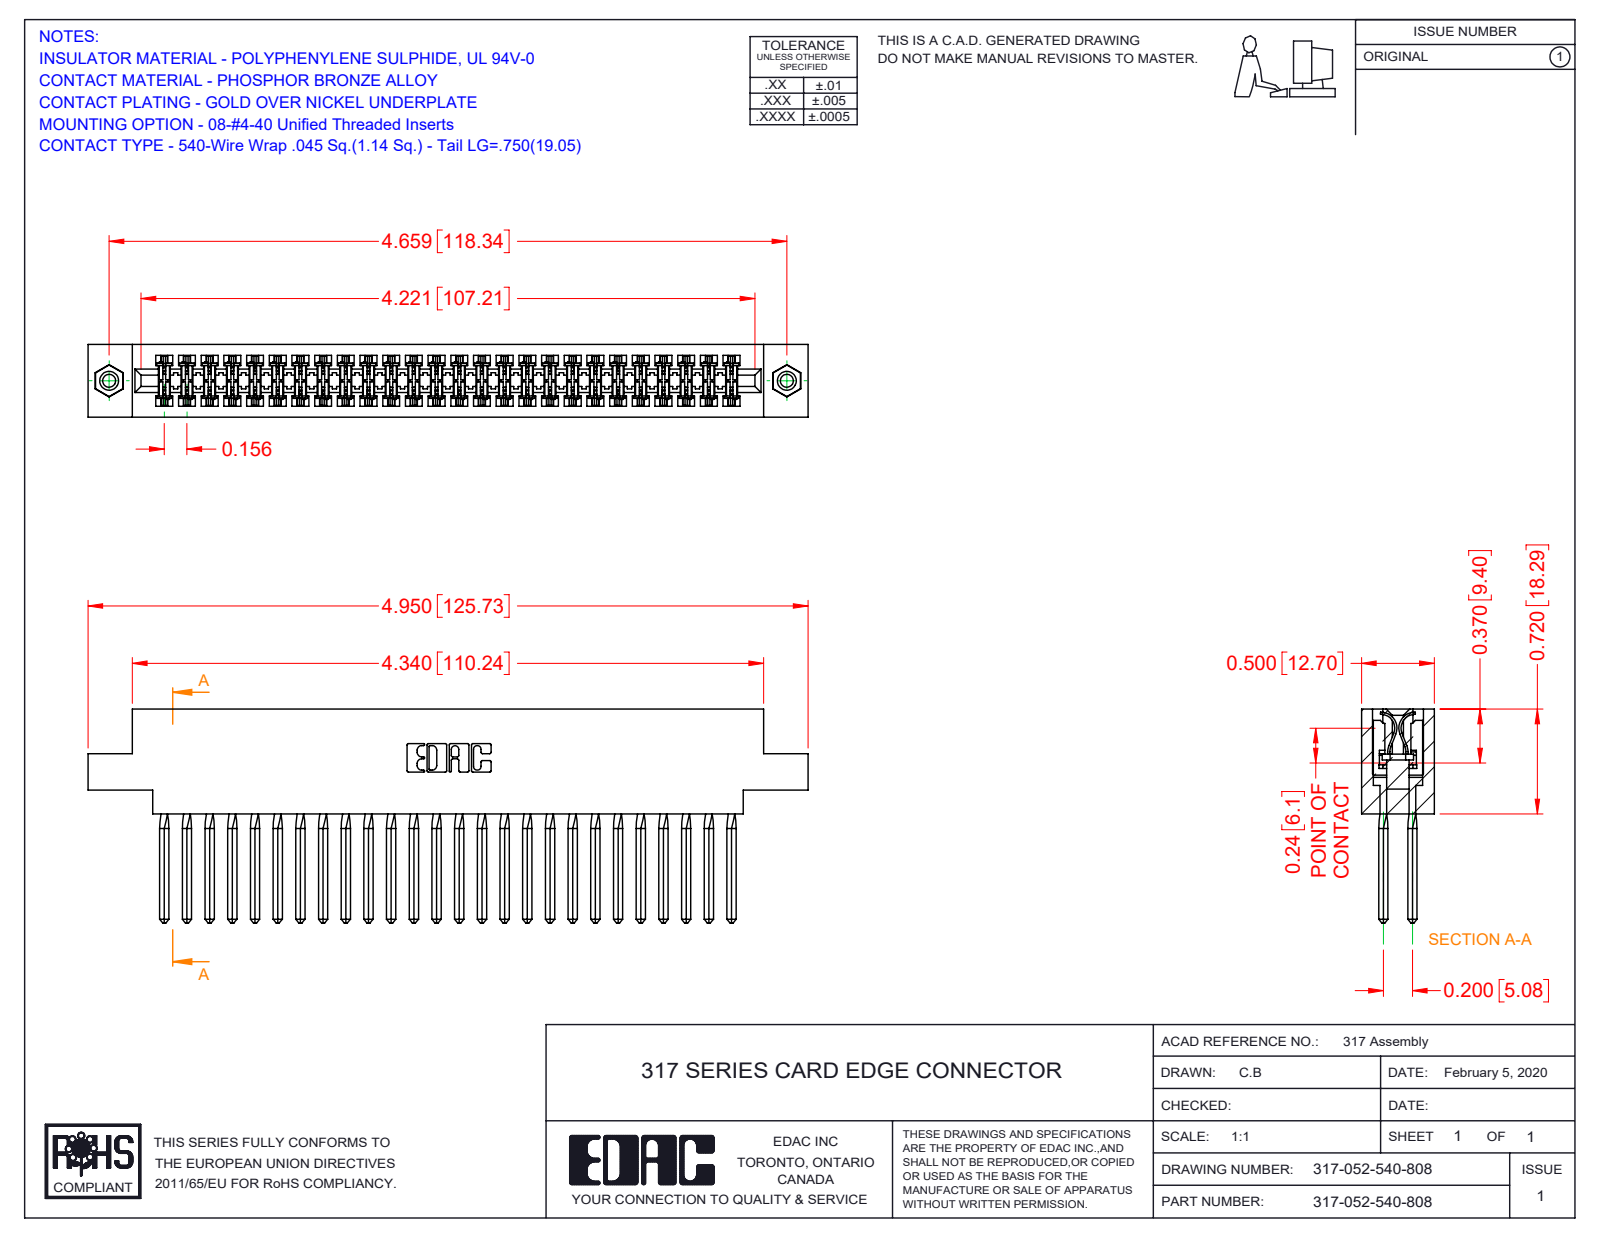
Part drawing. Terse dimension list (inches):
name: 317 Part_.156 Dia - TI; 317-052-540-808; 345-250-001_345-250-003-102; 317-290-001_540
written by: SolidWorks 2016 (CONFIG_CONTROL_DESIGN)
unit: in
bodies: 55 solids, 4790 faces (3886 planar, 680 cylindrical, 224 other)
size: 4.95 × 1.47 × 0.5
volume: 1.254 in³; area: 46.6 in²
holes: 2× ⌀0.089, 2× ⌀0.125, 2× ⌀0.156
bosses: 2× ⌀0.155
rounds: 104× R0.015, 22× R0.01, 6× R0.007, 6× R0.031, 3× R0.026, 2× R0.095, 2× R0.1, 2× R0.11
face distances: 0.5, 0.075, 0.425, 0.35, 0.11, 0.195, 0.094, 0.2, 0.72, 0.115
hole spacings: 4.659
